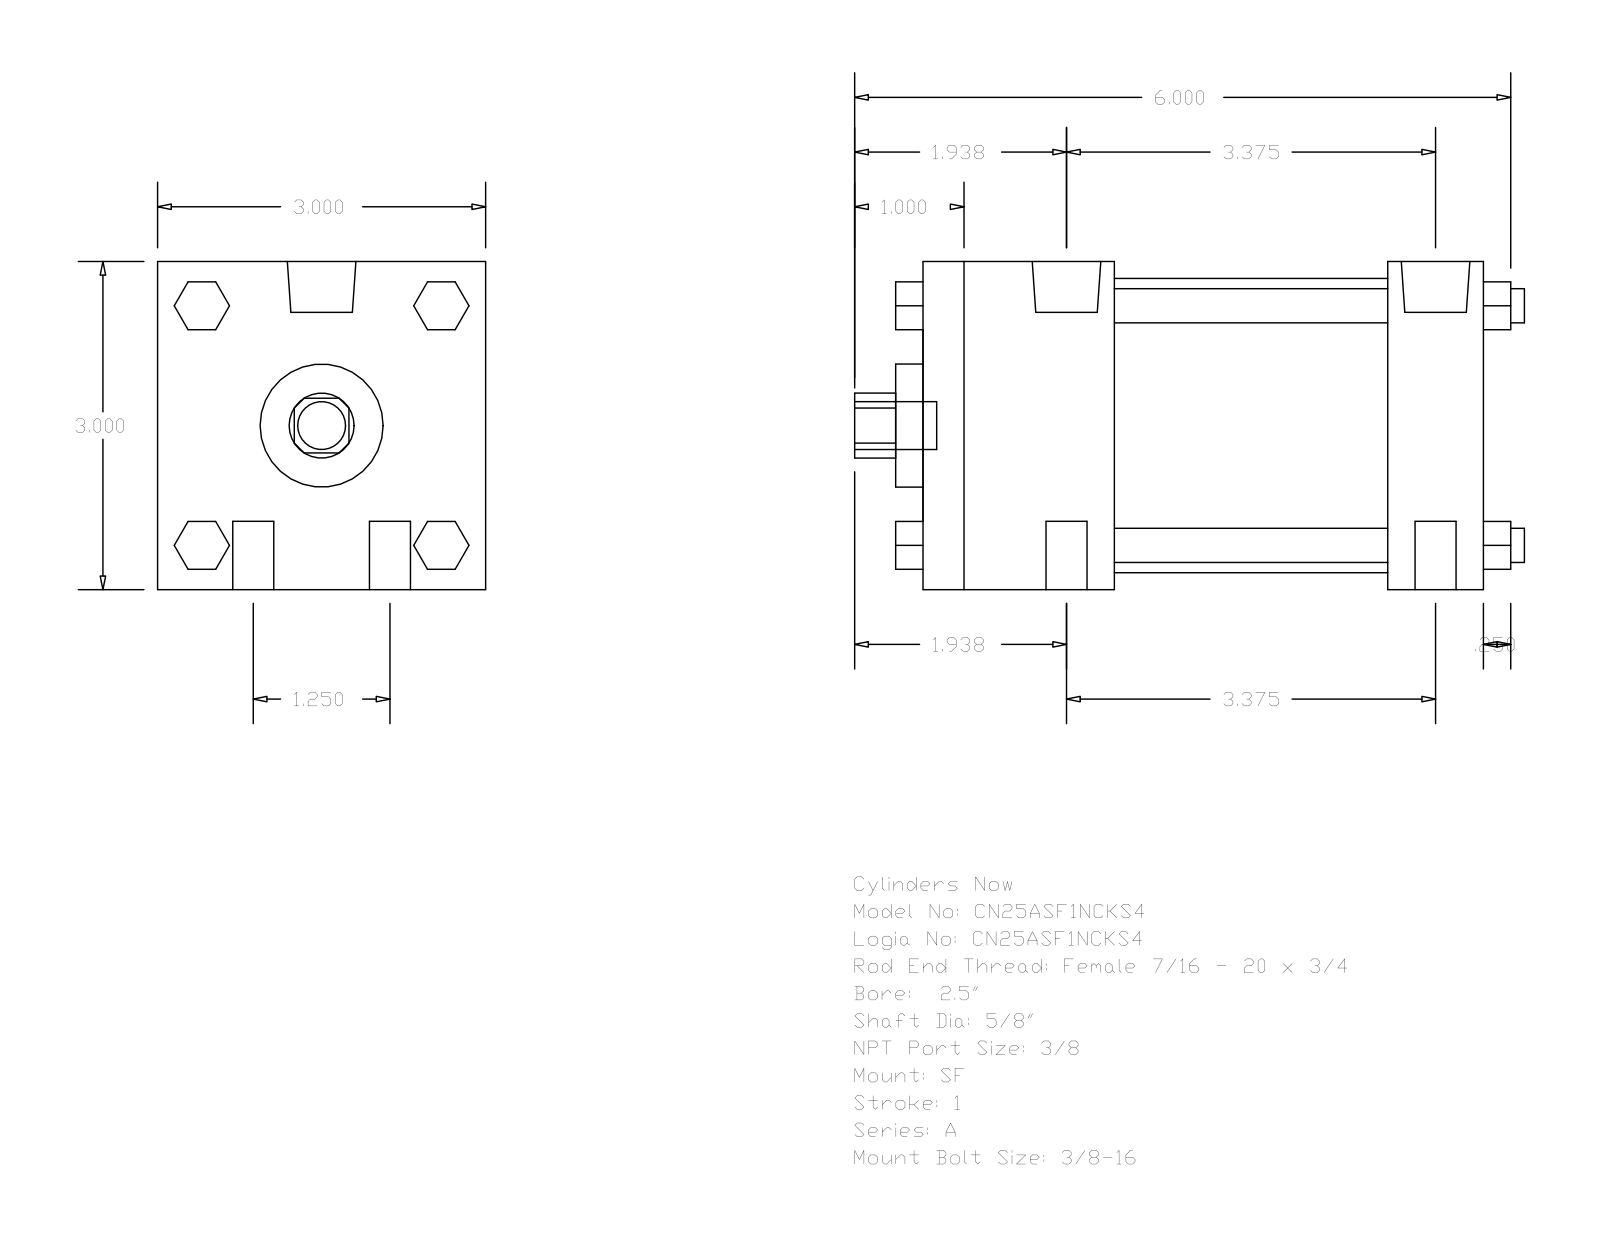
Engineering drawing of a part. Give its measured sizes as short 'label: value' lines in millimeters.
name: A_SF__0250_0.625
written by: GSSL Pune (CONFIG_CONTROL_DESIGN)
unit: mm
bodies: 0 solids, 124 faces (94 planar, 30 cylindrical, 0 other)
size: 155.57 × 76.2 × 76.2
holes: 1× ⌀15.88, 1× ⌀28.57, 1× ⌀68.33
bosses: 4× ⌀9.53, 4× ⌀7.94, 2× ⌀15.93, 2× ⌀5.56, 1× ⌀11.11
rounds: 1× R7.54
face distances: 76.2, 130.17, 63.5, 44.45, 107.95, 22.22, 85.72, 136.52, 6.35, 50.8
